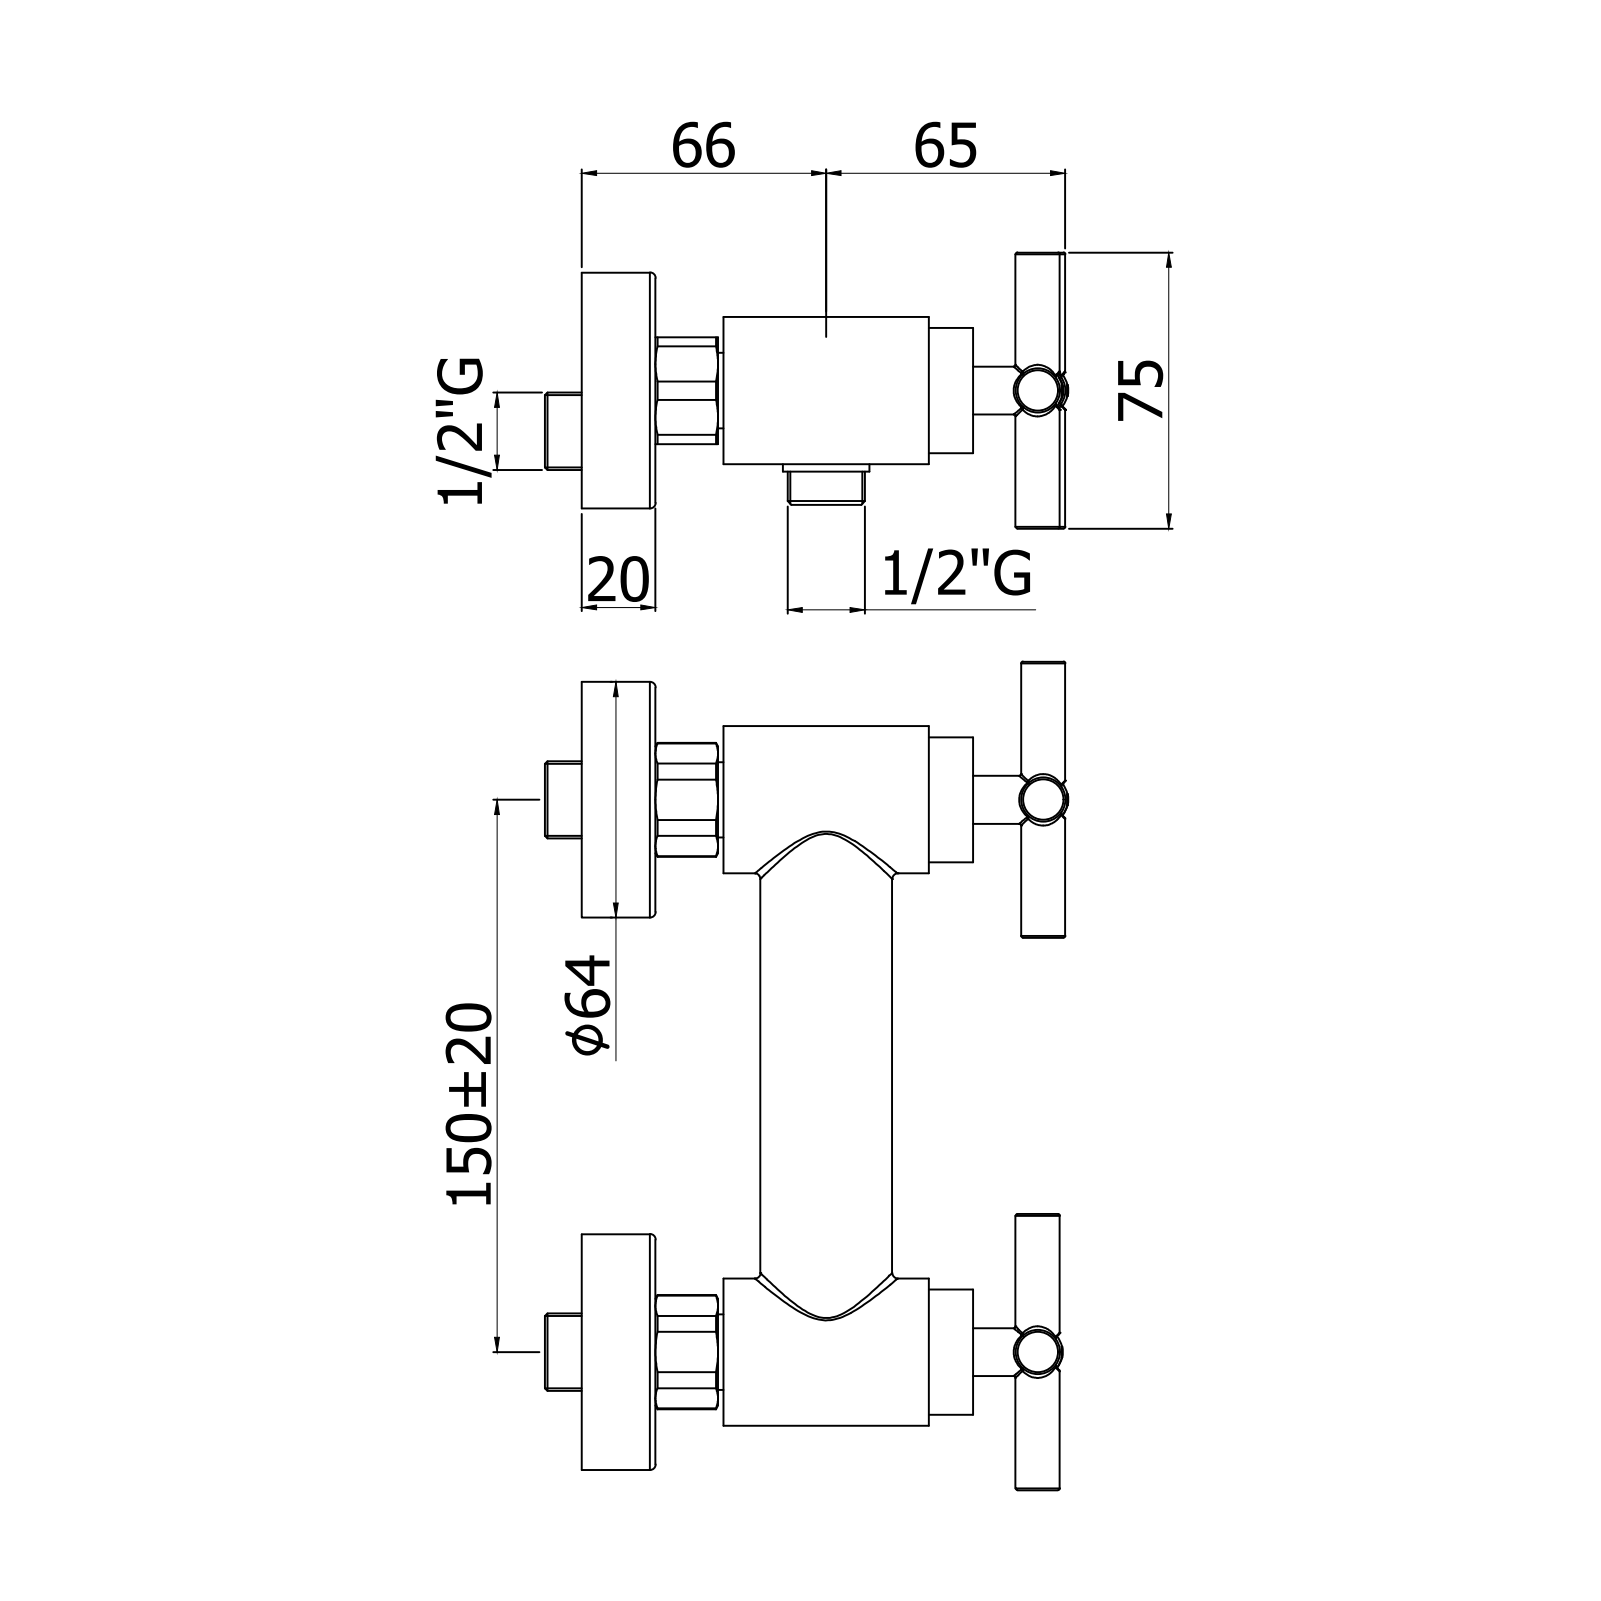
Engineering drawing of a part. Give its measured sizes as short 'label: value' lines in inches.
name: QTV168CR
written by: CREO PARAMETRIC BY PTC INC, 2020044 (CONFIG_CONTROL_DESIGN)
unit: in
bodies: 1 solid, 923 faces (443 planar, 258 cylindrical, 222 other)
size: 8.406 × 5.197 × 2.5
volume: 14.54 in³; area: 187.4 in²
holes: 4× ⌀0.374, 2× ⌀0.13, 2× ⌀0.177, 2× ⌀0.276, 2× ⌀0.315, 2× ⌀0.346, 2× ⌀0.394, 2× ⌀0.531, 2× ⌀0.642, 2× ⌀0.657, 2× ⌀0.709, 2× ⌀0.787
bosses: 4× ⌀0.807, 4× ⌀0.472, 2× ⌀2.5, 2× ⌀1.614, 2× ⌀1.063, 2× ⌀1.031, 2× ⌀0.945, 2× ⌀0.732
rounds: 34× R0.004, 4× R0.02, 4× R0.039, 4× R0.236, 2× R0.118, 2× R0.37, 1× R0.203
face distances: 0.024, 0.394, 2.669, 0.752, 0.728, 1.122, 2.276, 3.421, 3.398, 1.299
hole spacings: 5.906
